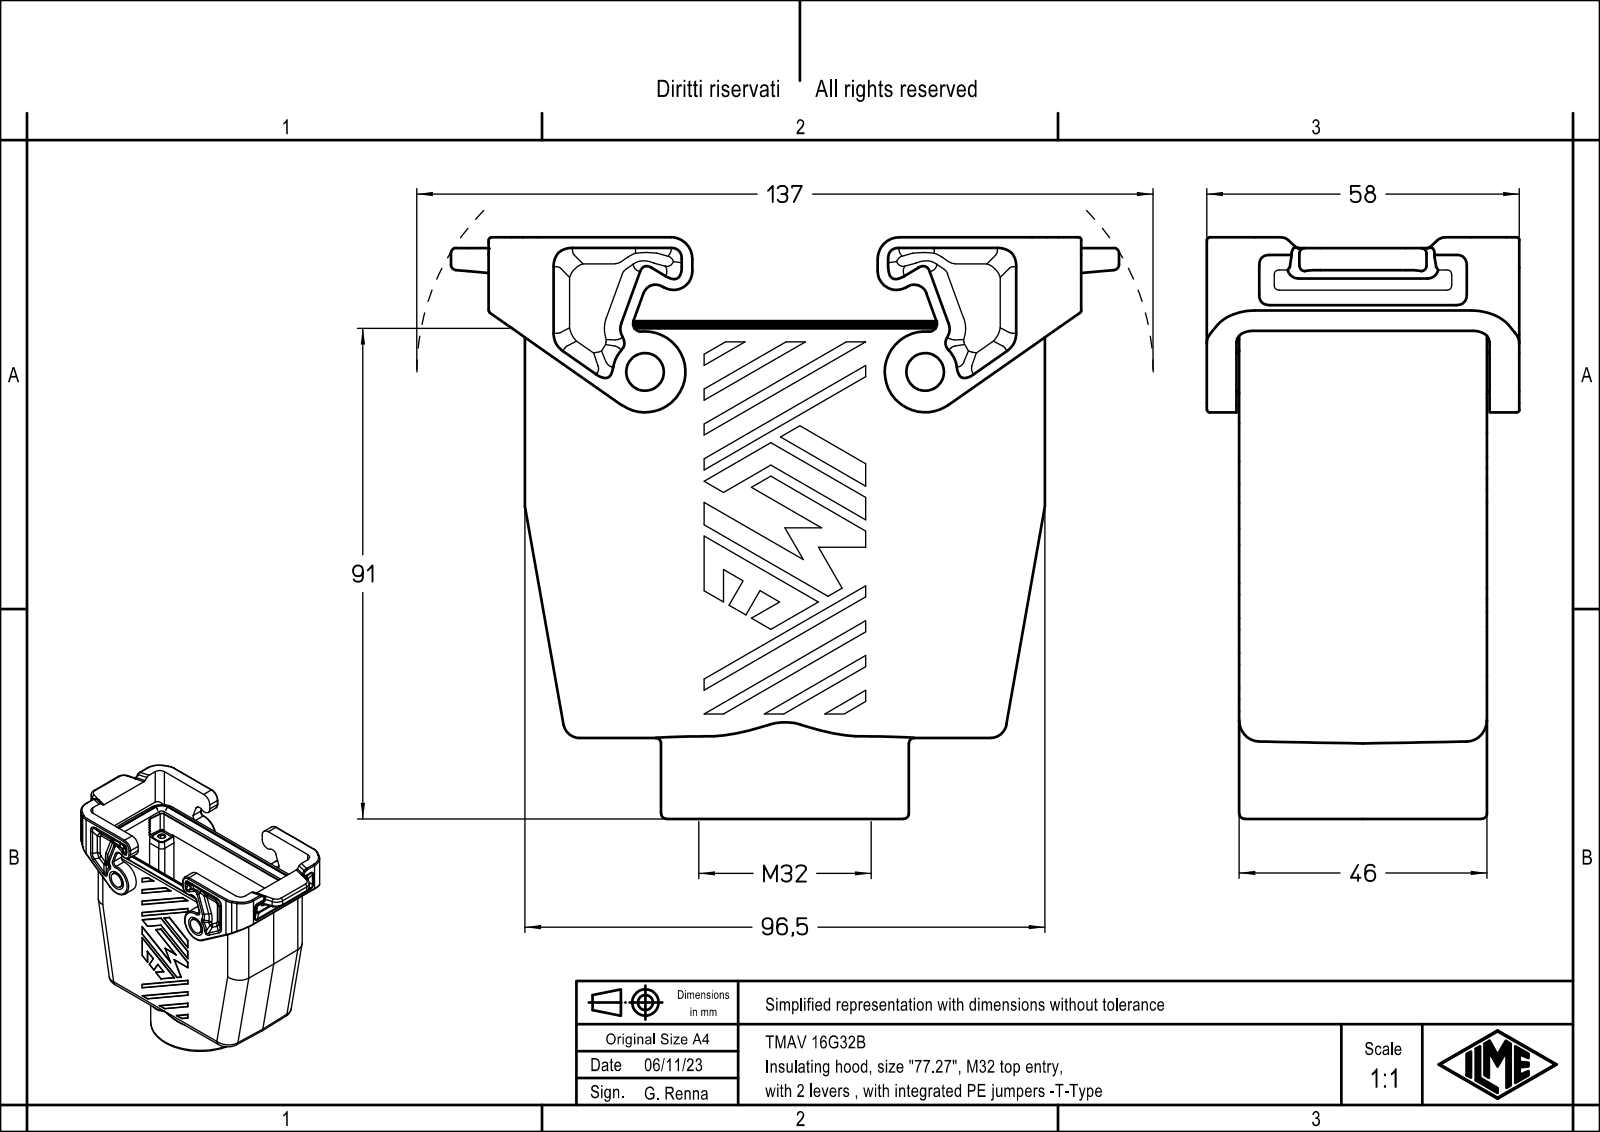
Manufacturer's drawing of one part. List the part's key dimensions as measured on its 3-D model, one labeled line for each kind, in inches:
Part name (STEP PRODUCT): TMAV 16G32B
STEP written by: Creo Elements/Direct Modeling 20.1B 02-Apr-2019 (C) Parametric Technology GmbH (AUTOMOTIVE_DESIGN)
Units: inches
Bodies: 1 solid, 754 faces (374 planar, 318 cylindrical, 62 other)
Overall size (bounding box): 4.882 × 4.248 × 2.283
Volume: 9.866 in³ · Surface area: 100.2 in²
Round holes (diameter × count): ⌀0.138 ×4, ⌀1.102 ×1, ⌀1.205 ×1
Round bosses / shafts (diameter × count): ⌀0.276 ×2, ⌀1.811 ×1
Partial cylindrical surfaces — rounded edges, fillets, slot ends (radius × count): R0.006 ×88, R0.079 ×20, R0.118 ×20, R0.059 ×18, R0.039 ×16, R0.051 ×12, R0.236 ×8, R0.276 ×8
Main face-to-face distances: 0.213, 1.598, 1.386, 1.811, 0.02, 0.232, 1.618, 1.831, 0.217, 0.236
Hole centre spacings: 1.615, 1.063, 3.051, 3.231
